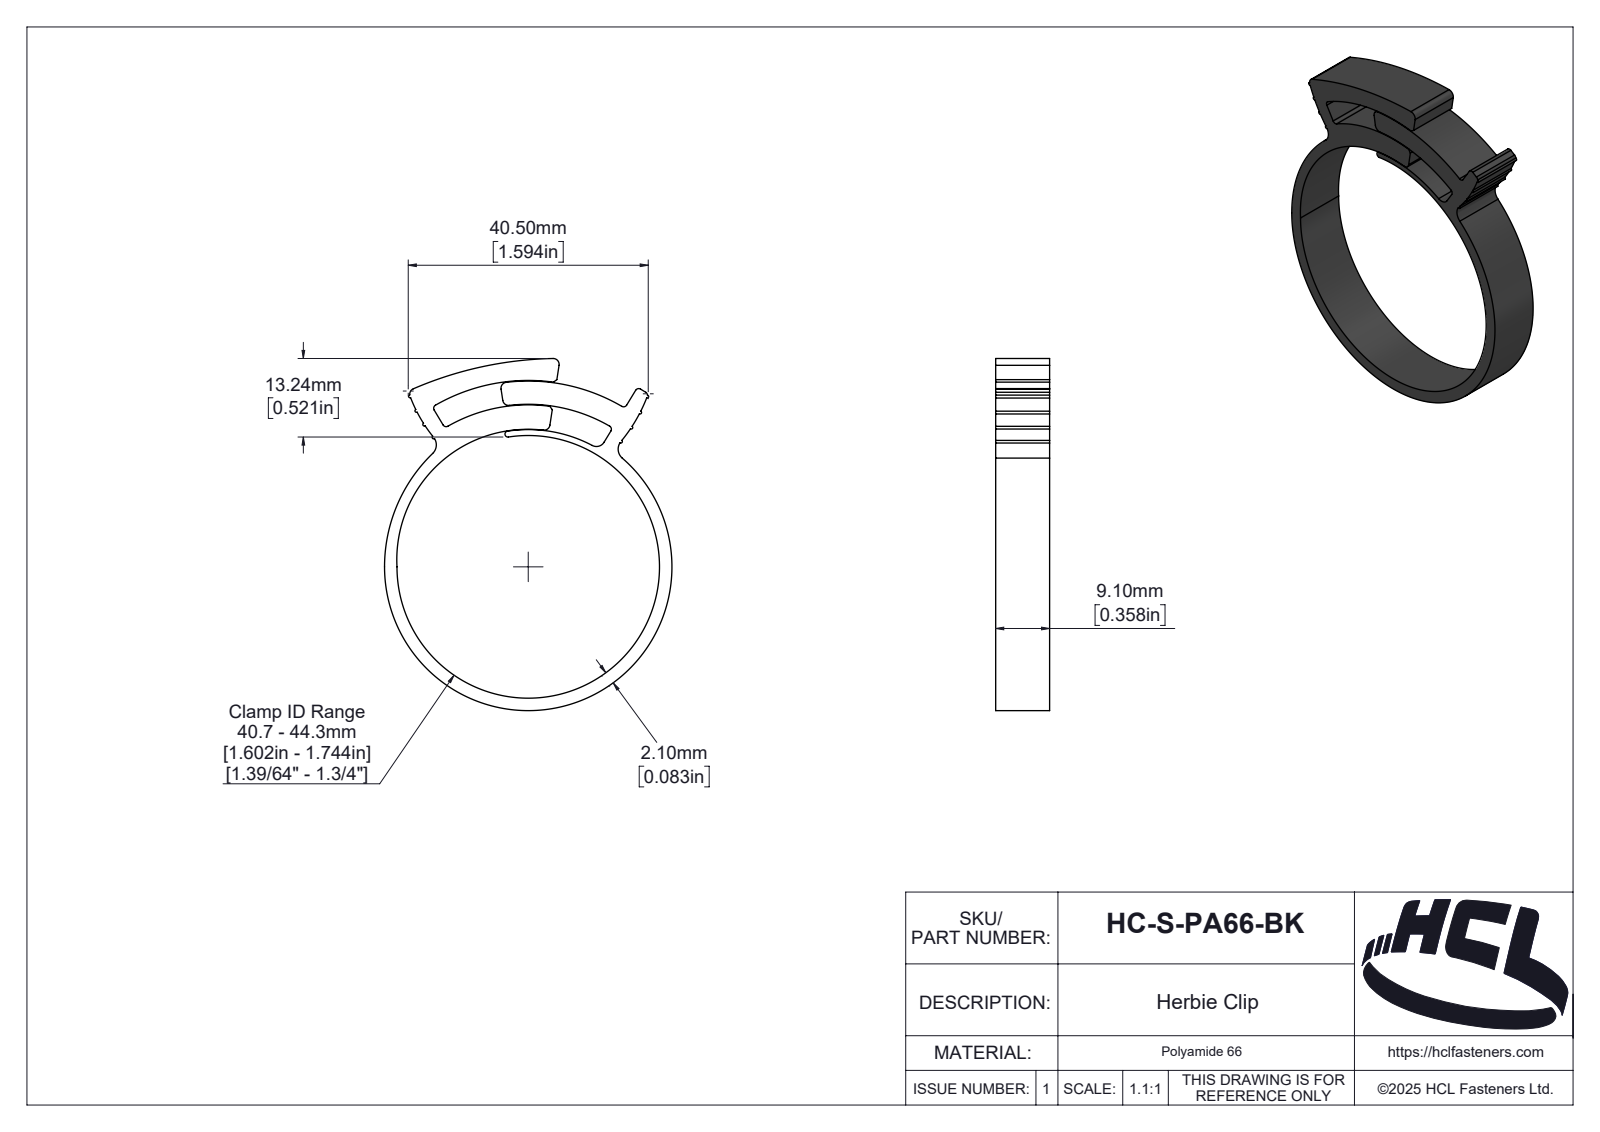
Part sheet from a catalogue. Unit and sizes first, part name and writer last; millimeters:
Units: millimetres
Overall size (bounding box): 59.39 × 48.5 × 9.1
Partial cylindrical surfaces — rounded edges, fillets, slot ends (radius × count): R0.25 ×8, R0.6 ×6, R1 ×5, R2 ×2, R0.17 ×1, R0.5 ×1, R0.67 ×1, R0.84 ×1
Main face-to-face distances: 9.1
Volume: 5 049 mm³ · Surface area: 5 117 mm²
Bodies: 1 solid, 162 faces (13 planar, 100 cylindrical, 49 other)
Part name (STEP PRODUCT): HC-S-PA66-BK
STEP written by: SolidWorks 2025 (AUTOMOTIVE_DESIGN)
